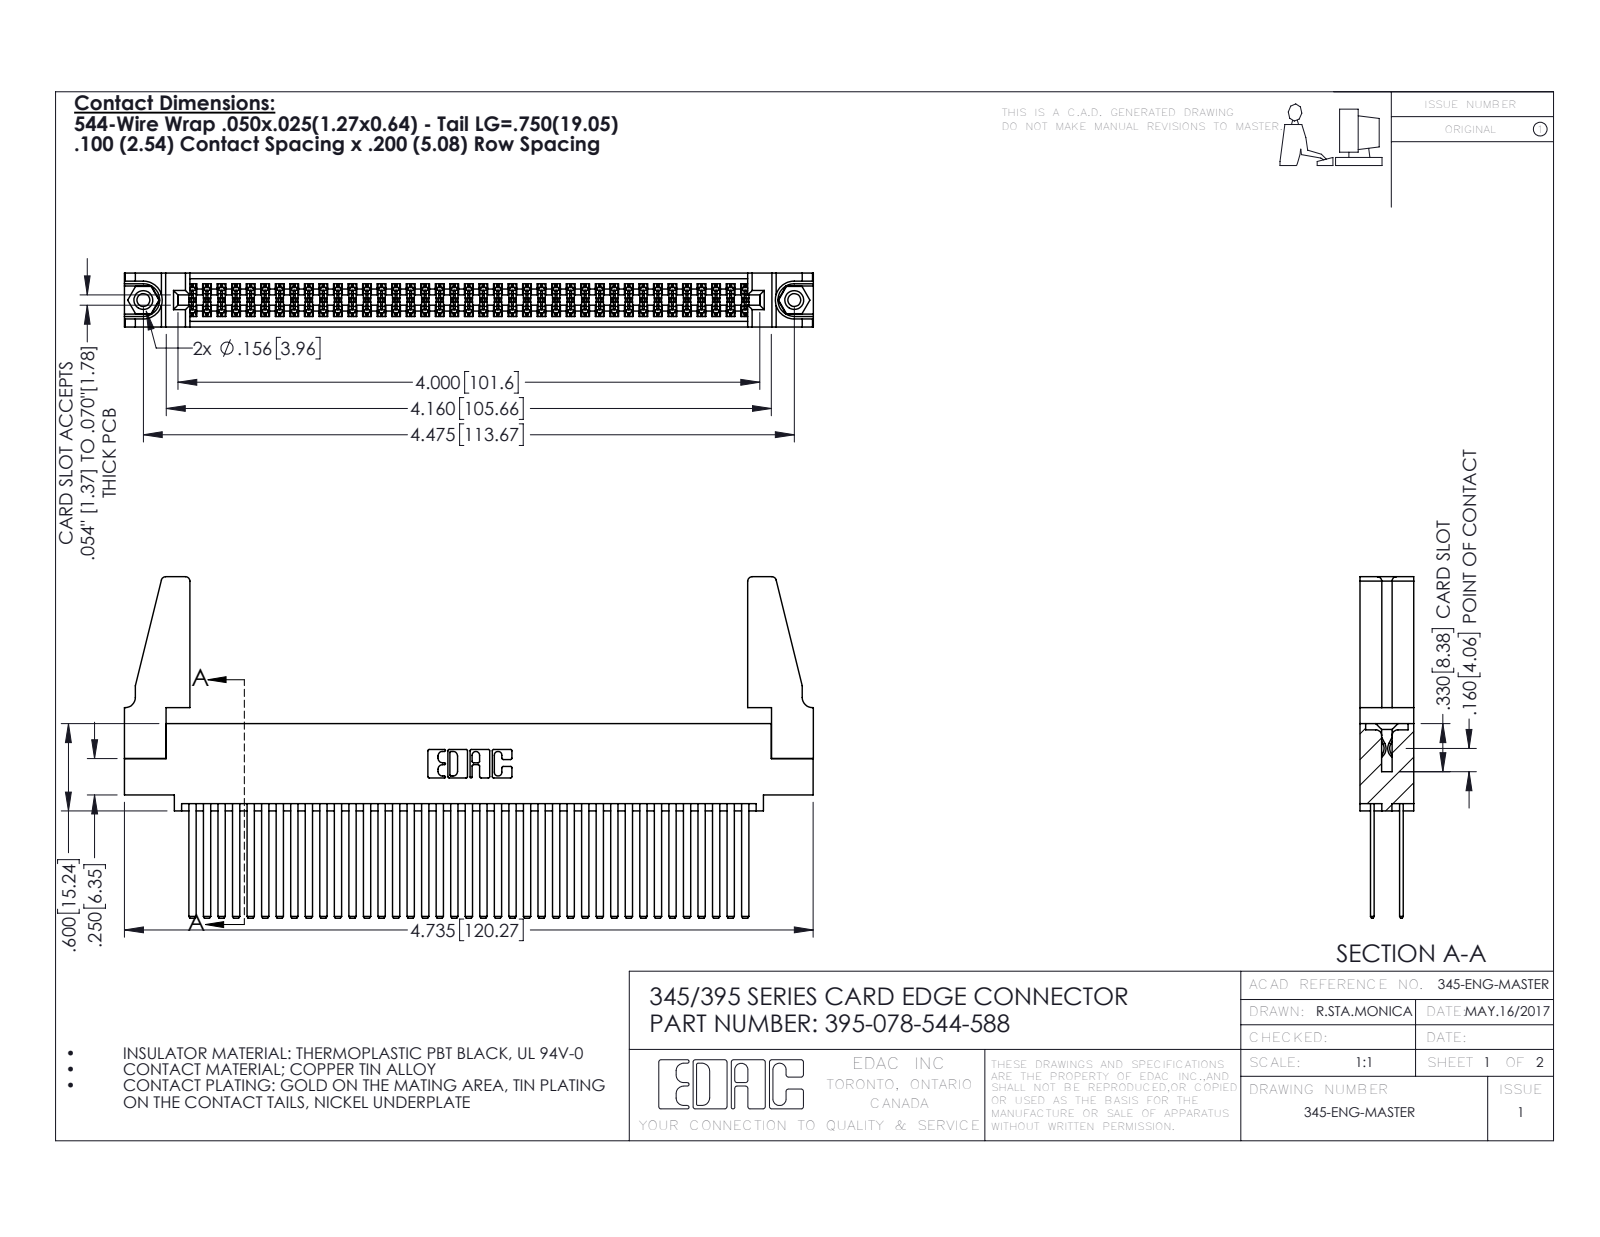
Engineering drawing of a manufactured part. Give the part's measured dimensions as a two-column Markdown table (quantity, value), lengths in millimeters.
| quantity | value |
| --- | --- |
| part name | 345-250-001_345-250-001-102; 345-220-078_345-220-088; 395-078-544-588; 345-292-001_345-293-144 (+1 more) |
| STEP written by | SolidWorks 2016 (CONFIG_CONTROL_DESIGN) |
| units | millimeters |
| bodies | 83 solids, 3686 faces (2418 planar, 1252 cylindrical, 16 other) |
| overall size | 120.3 × 59.6 × 9.4 |
| volume | 15 900 mm³ |
| surface area | 25 100 mm² |
| round holes (diameter × count) | 2.3 × 2, 3.2 × 2, 4 × 2, 1.6 × 1 |
| round bosses / shafts (diameter × count) | 3.9 × 2 |
| partial cylindrical surfaces (radius × count) | 0.2 × 117, 0.3 × 22, 0.8 × 8, 0.2 × 6, 0.8 × 6, 0.7 × 3, 0.4 × 2, 0.5 × 2 |
| main face-to-face distances | 1.8, 7.6, 5.1, 2.5, 6.9, 0.6, 5.7, 9.4, 4.4, 3.8 |
| hole center spacings | 6.9, 107.7, 113.7 |
